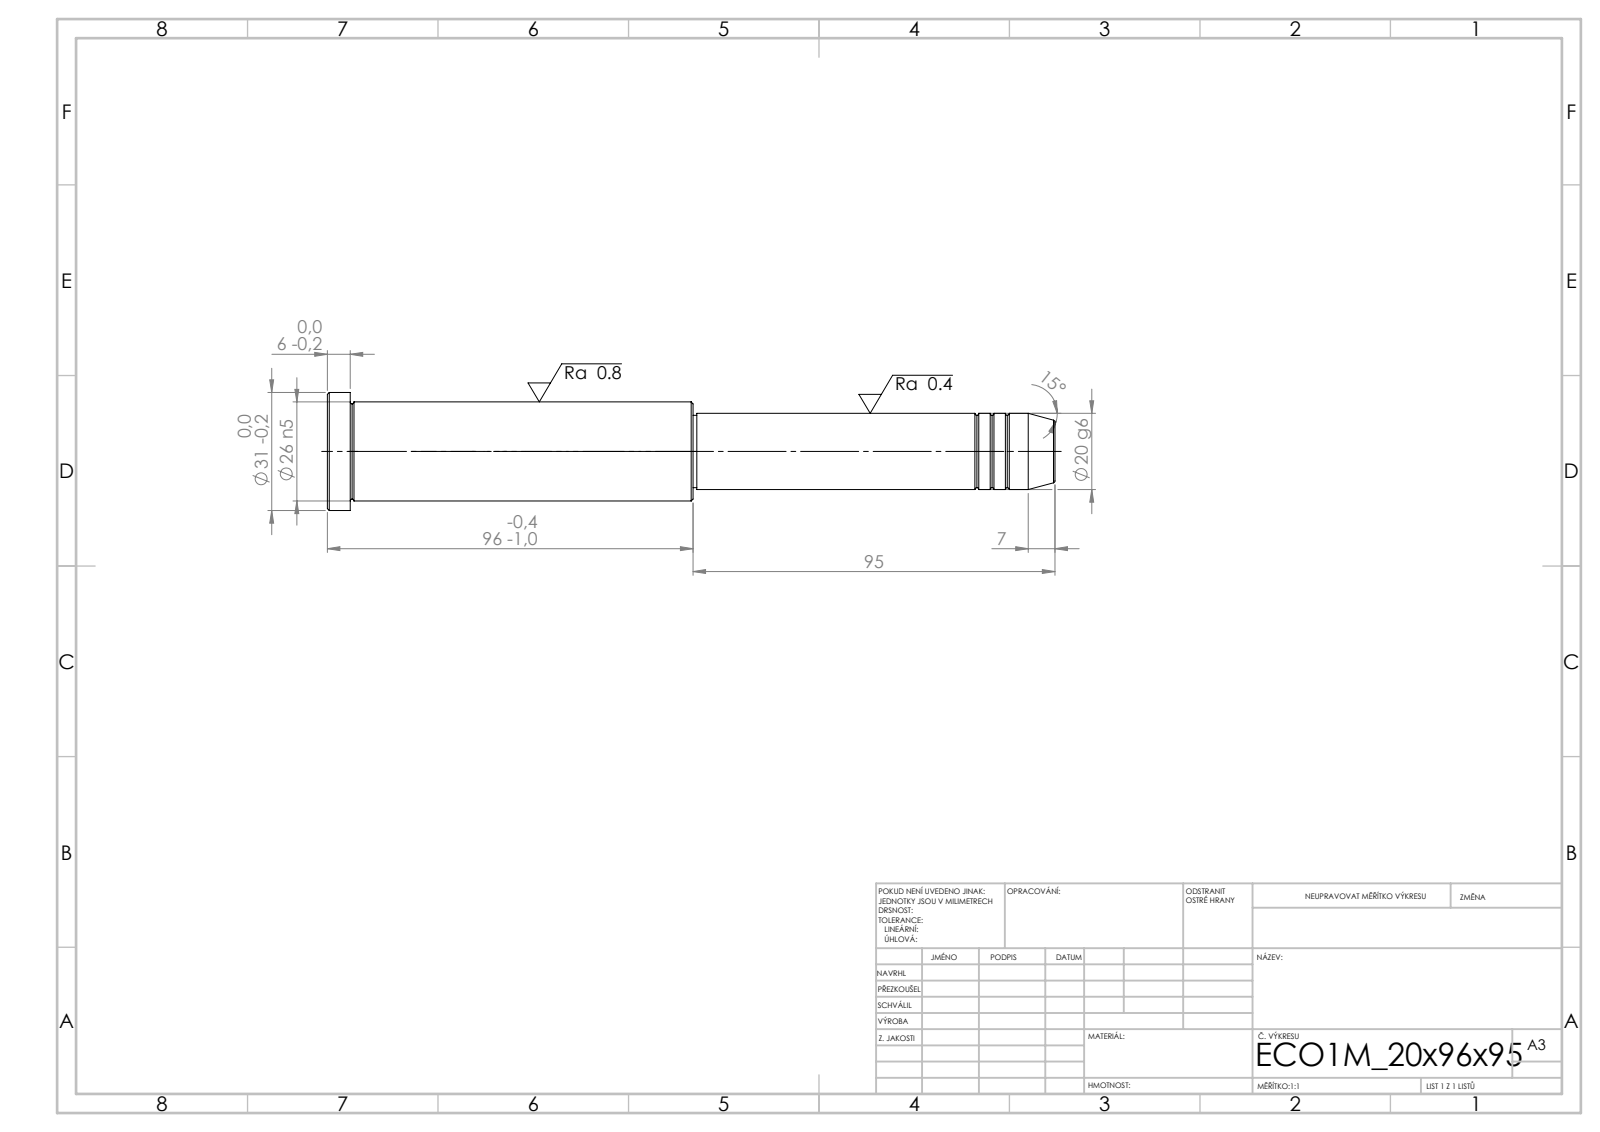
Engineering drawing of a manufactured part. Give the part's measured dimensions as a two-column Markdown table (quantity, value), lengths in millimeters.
| quantity | value |
| --- | --- |
| STEP written by | SolidWorks 2019 (CONFIG_CONTROL_DESIGN) |
| units | millimeters |
| bodies | 1 solid, 43 faces (5 planar, 14 cylindrical, 24 other) |
| overall size | 191 × 31 × 31 |
| volume | 81 612 mm³ |
| surface area | 15 421 mm² |
| round bosses / shafts (diameter × count) | 31 × 1, 26 × 1, 20 × 1, 19 × 1 |
| main face-to-face distances | 6, 90, 96, 95, 185, 191, 94, 1, 91, 97 |
